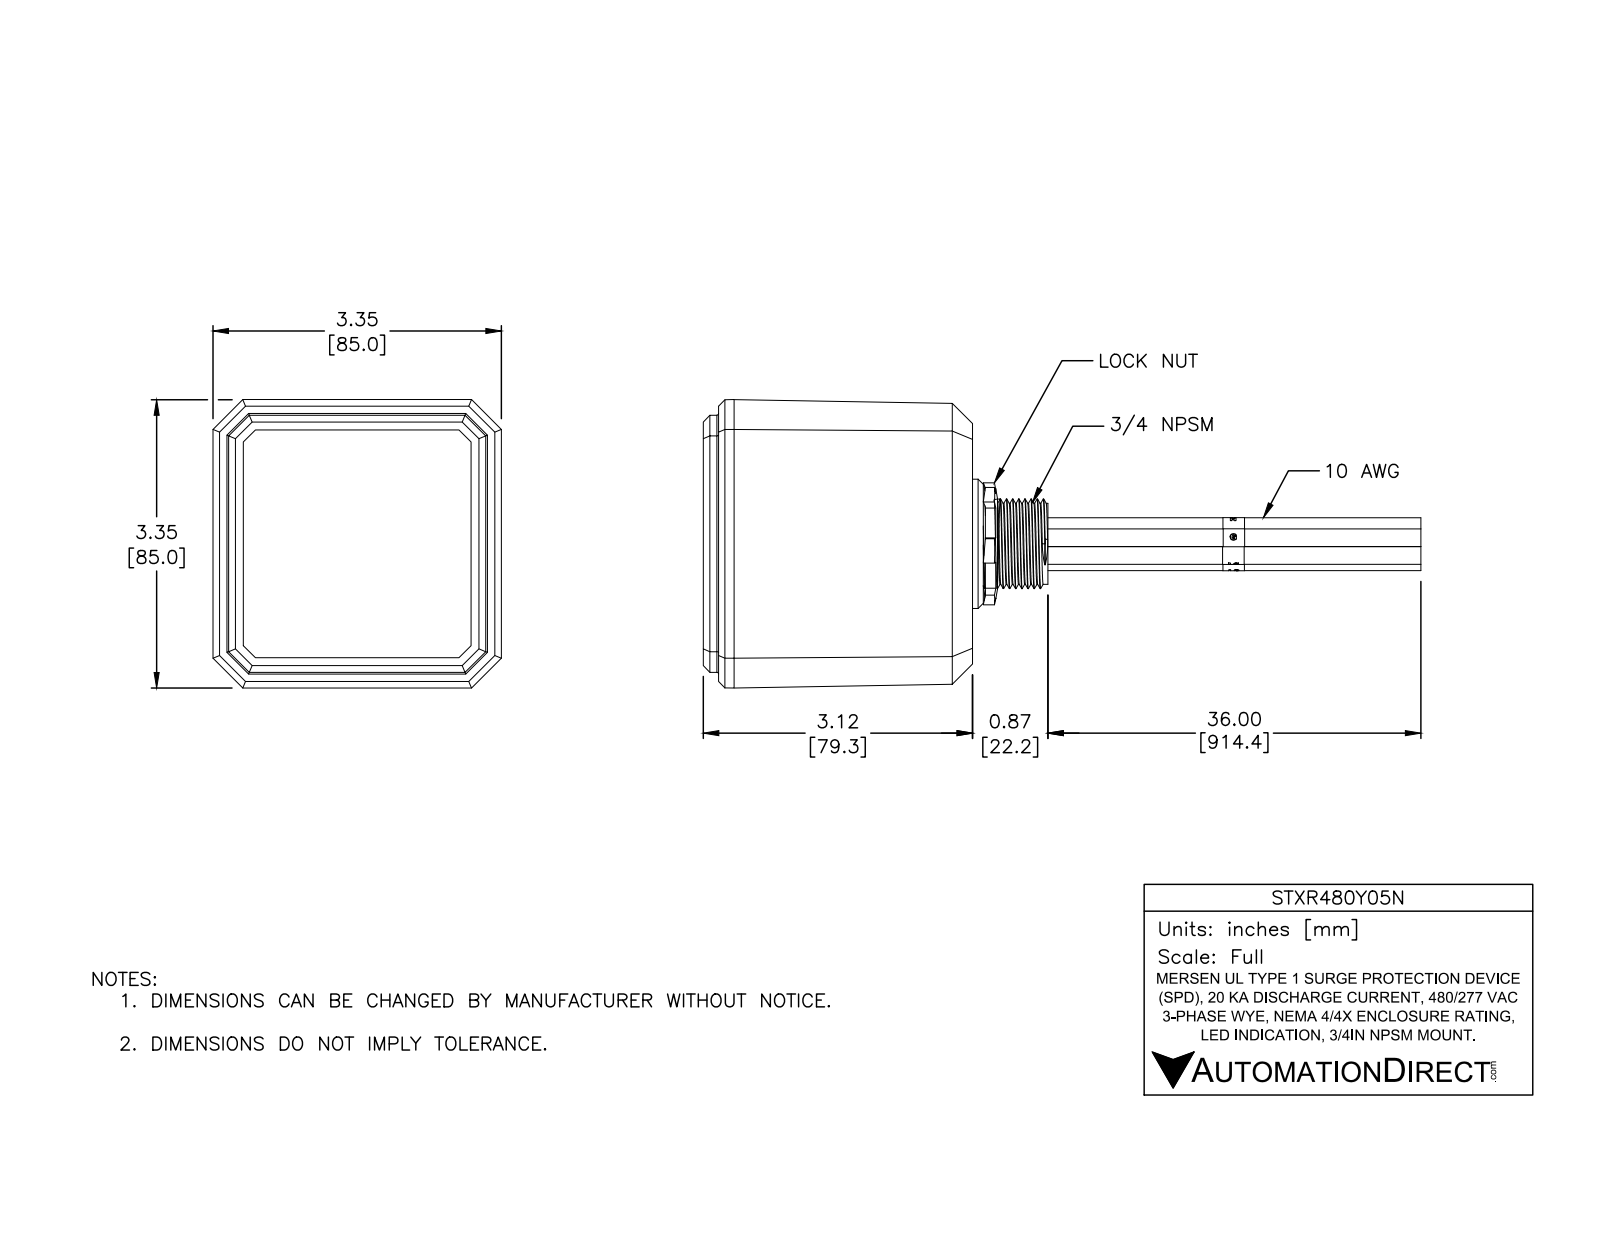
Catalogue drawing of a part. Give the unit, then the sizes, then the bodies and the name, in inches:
Units: inches
Overall size (bounding box): 8.327 × 3.347 × 3.347
Round holes (diameter × count): ⌀1 ×1
Round bosses / shafts (diameter × count): ⌀0.205 ×15, ⌀0.205 ×3, ⌀0.145 ×3, ⌀0.145 ×2, ⌀1.5 ×1, ⌀0.94 ×1
Partial cylindrical surfaces — rounded edges, fillets, slot ends (radius × count): R0.015 ×16, R0.02 ×8, R0.1 ×8, R0.04 ×4, R0.31 ×1, R0.639 ×1
Main face-to-face distances: 0.125, 0.125, 0.12, 2.989, 3.109, 2.864, 2.984, 2.766, 2.641, 0.223
Volume: 8.453 in³ · Surface area: 148.8 in²
Bodies: 8 solids, 525 faces (318 planar, 123 cylindrical, 84 other)
Part name (STEP PRODUCT): STXR480Y05N
STEP written by: SolidWorks 2016 (AUTOMOTIVE_DESIGN)
